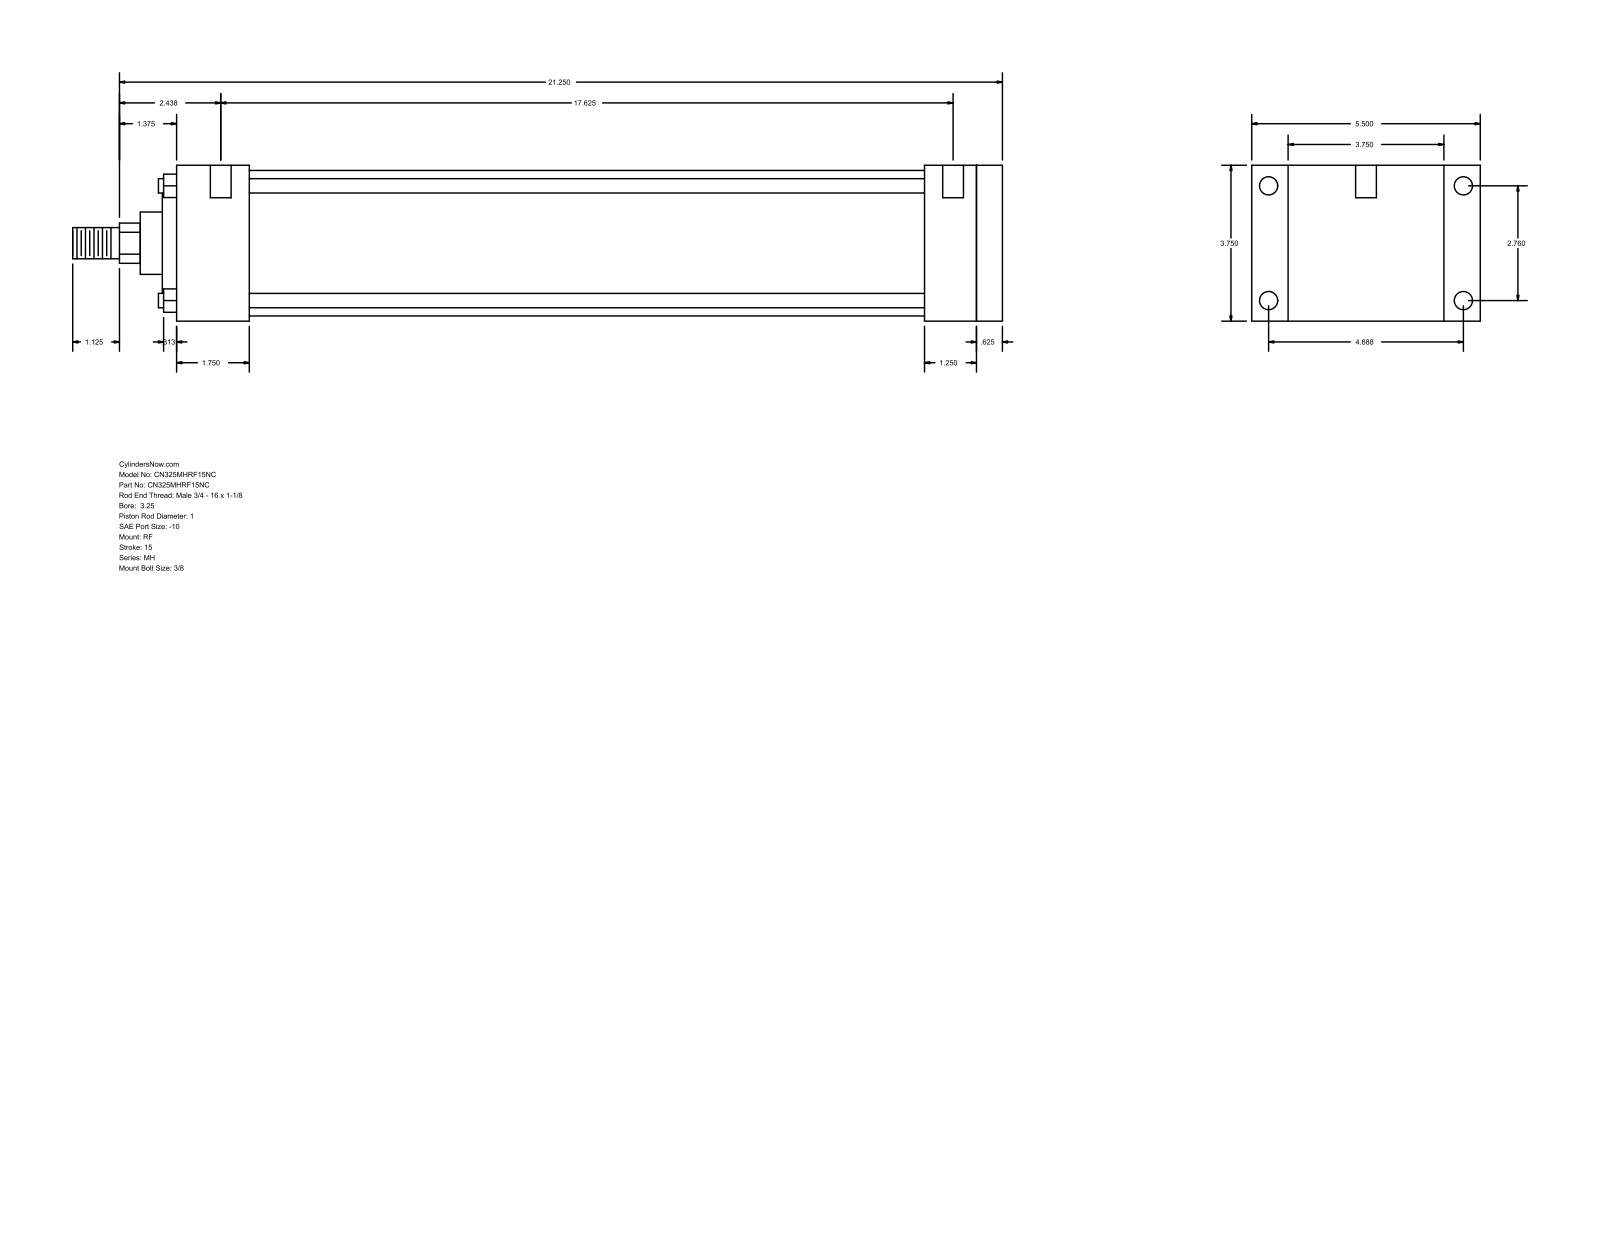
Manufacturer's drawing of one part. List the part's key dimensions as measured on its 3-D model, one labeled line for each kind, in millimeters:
Part name (STEP PRODUCT): MH_RF__0325_1
STEP written by: GSSL Pune (CONFIG_CONTROL_DESIGN)
Units: millimetres
Bodies: 0 solids, 94 faces (65 planar, 29 cylindrical, 0 other)
Overall size (bounding box): 568.33 × 139.7 × 95.25
Round holes (diameter × count): ⌀5.56 ×4, ⌀11.13 ×4, ⌀12.7 ×2
Round bosses / shafts (diameter × count): ⌀8.76 ×4, ⌀88.9 ×1, ⌀60.33 ×1, ⌀38.1 ×1, ⌀25.4 ×1, ⌀19.05 ×1
Partial cylindrical surfaces — rounded edges, fillets, slot ends (radius × count): R12.29 ×1
Main face-to-face distances: 95.24, 504.83, 488.96, 15.87, 22.23, 117.47, 44.46, 444.5, 460.37, 457.2
Hole centre spacings: 70.1, 119.06, 138.16, 454.02, 1.58, 4.76, 447.68, 449.26
